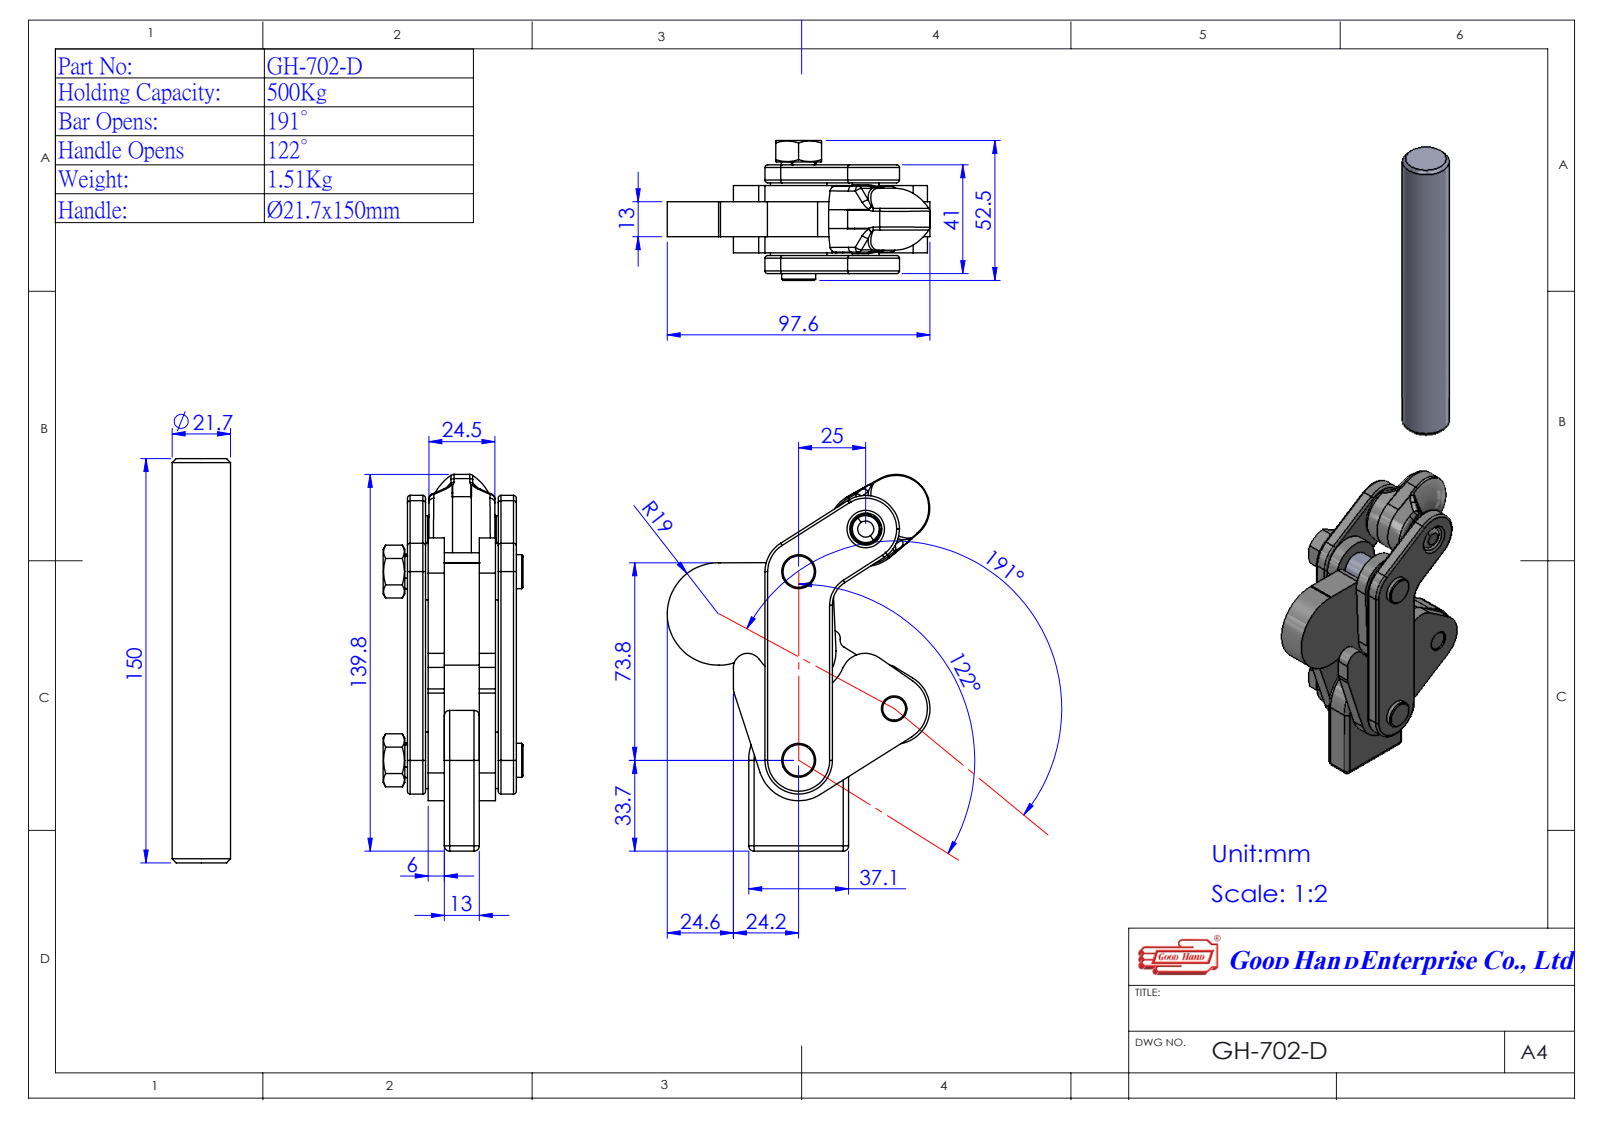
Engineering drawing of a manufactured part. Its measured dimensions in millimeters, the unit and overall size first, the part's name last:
Units: millimetres
Overall size (bounding box): 291.43 × 97.92 × 51.9
Round holes (diameter × count): ⌀9.5 ×3, ⌀9.6 ×1, ⌀11 ×1, ⌀12.7 ×1, ⌀16.9 ×1
Round bosses / shafts (diameter × count): ⌀9.52 ×3, ⌀21 ×2, ⌀12.6 ×2, ⌀21.7 ×1, ⌀14 ×1, ⌀10 ×1
Partial cylindrical surfaces — rounded edges, fillets, slot ends (radius × count): R12.5 ×5, R3 ×4, R5 ×3, R10 ×2, R15 ×2, R19 ×2, R5.25 ×1, R9 ×1
Main face-to-face distances: 13, 7, 20, 1, 6, 26, 19, 7.7, 33.7, 32.7
Hole centre spacings: 29.49, 30, 39.97, 40.05, 40.3, 51.47, 61.97, 67.46
Volume: 195 081 mm³ · Surface area: 78 466 mm²
Bodies: 7 solids, 196 faces (80 planar, 94 cylindrical, 22 other)
Part name (STEP PRODUCT): 4702D152; GH-702-D; Group2^GH-702-D(簡化); Group5^GH-702-D(簡化) (+4 more)
STEP written by: SolidWorks 2016 (AUTOMOTIVE_DESIGN)
